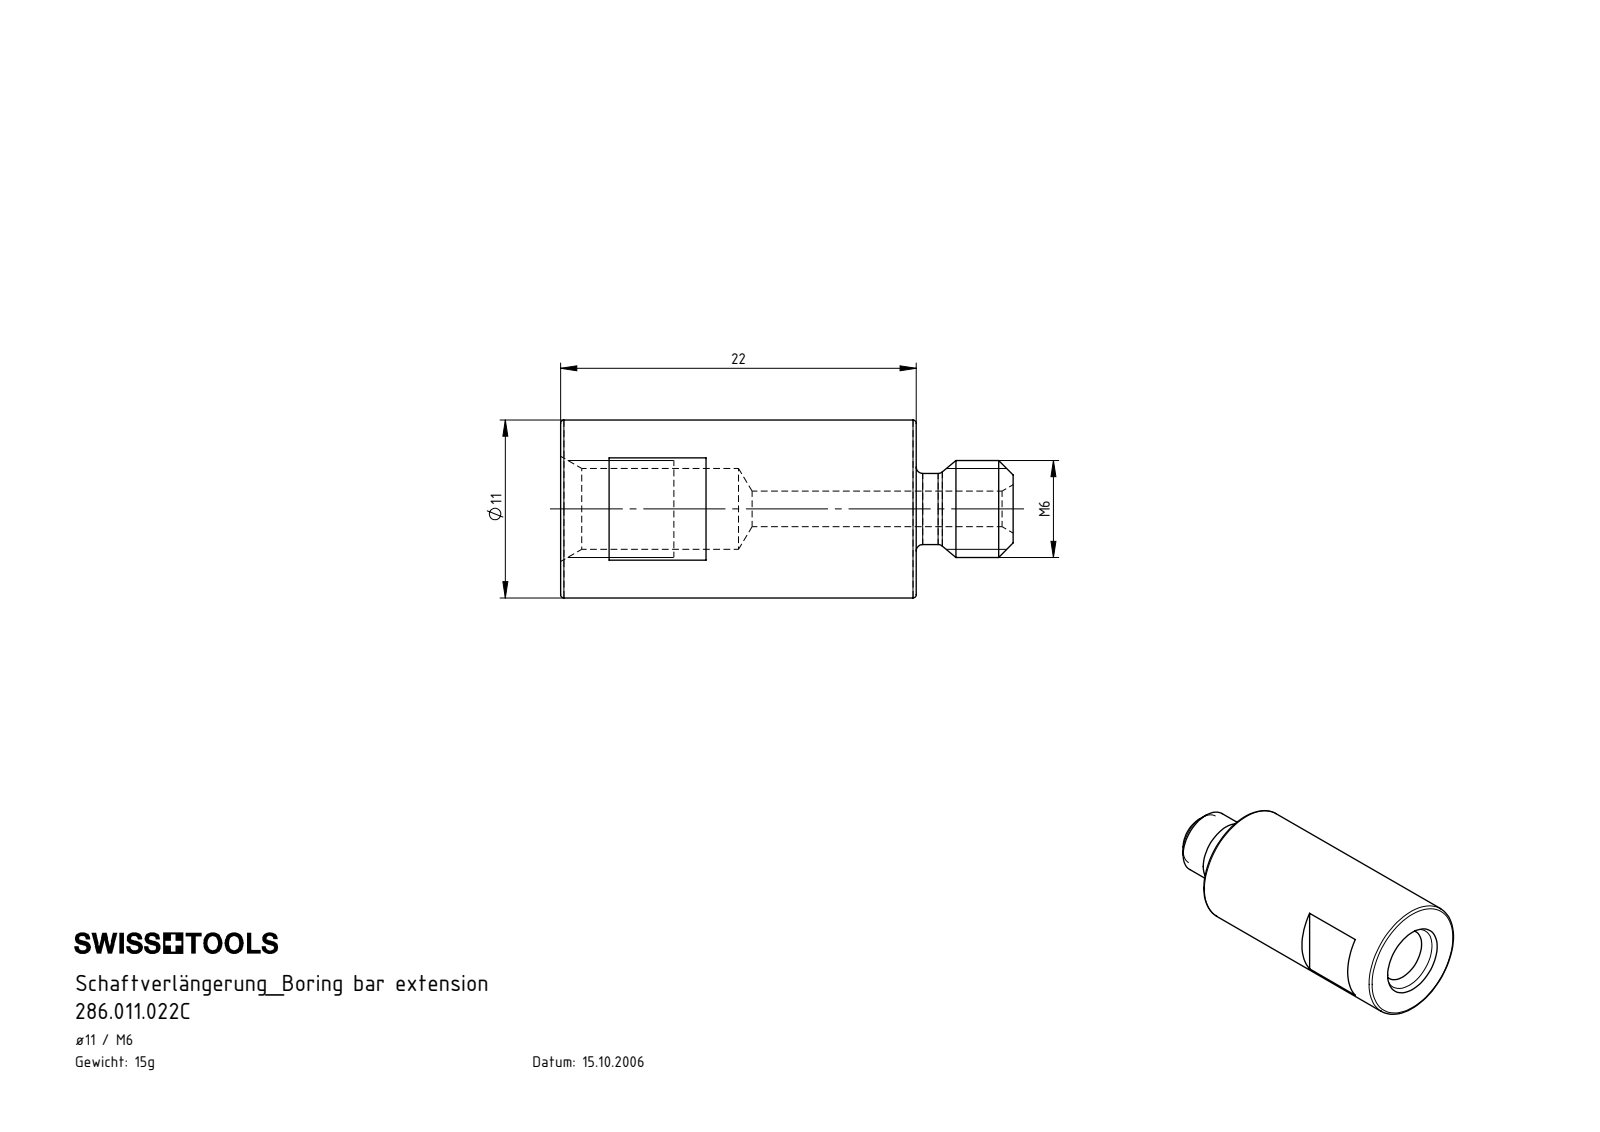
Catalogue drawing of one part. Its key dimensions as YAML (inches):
part_name: "286.011.022C"
step_written_by: "SolidWorks 2022 (CONFIG_CONTROL_DESIGN)"
units: inches
bodies: {solids: 1, faces: 37, planar: 9, cylindrical: 10, other: 18}
overall_size: [1.102, 0.433, 0.433]
volume: 0.115
surface_area: 2.069
round_holes:
  - {diameter: 0.087, count: 1}
  - {diameter: 0.197, count: 1}
round_bosses_or_shafts:
  - {diameter: 0.433, count: 1}
  - {diameter: 0.236, count: 1}
  - {diameter: 0.173, count: 1}
face_to_face_distances: [0.866, 0.354, 0.748, 0.236, 0.118, 0.512, 0.984, 1.102]
